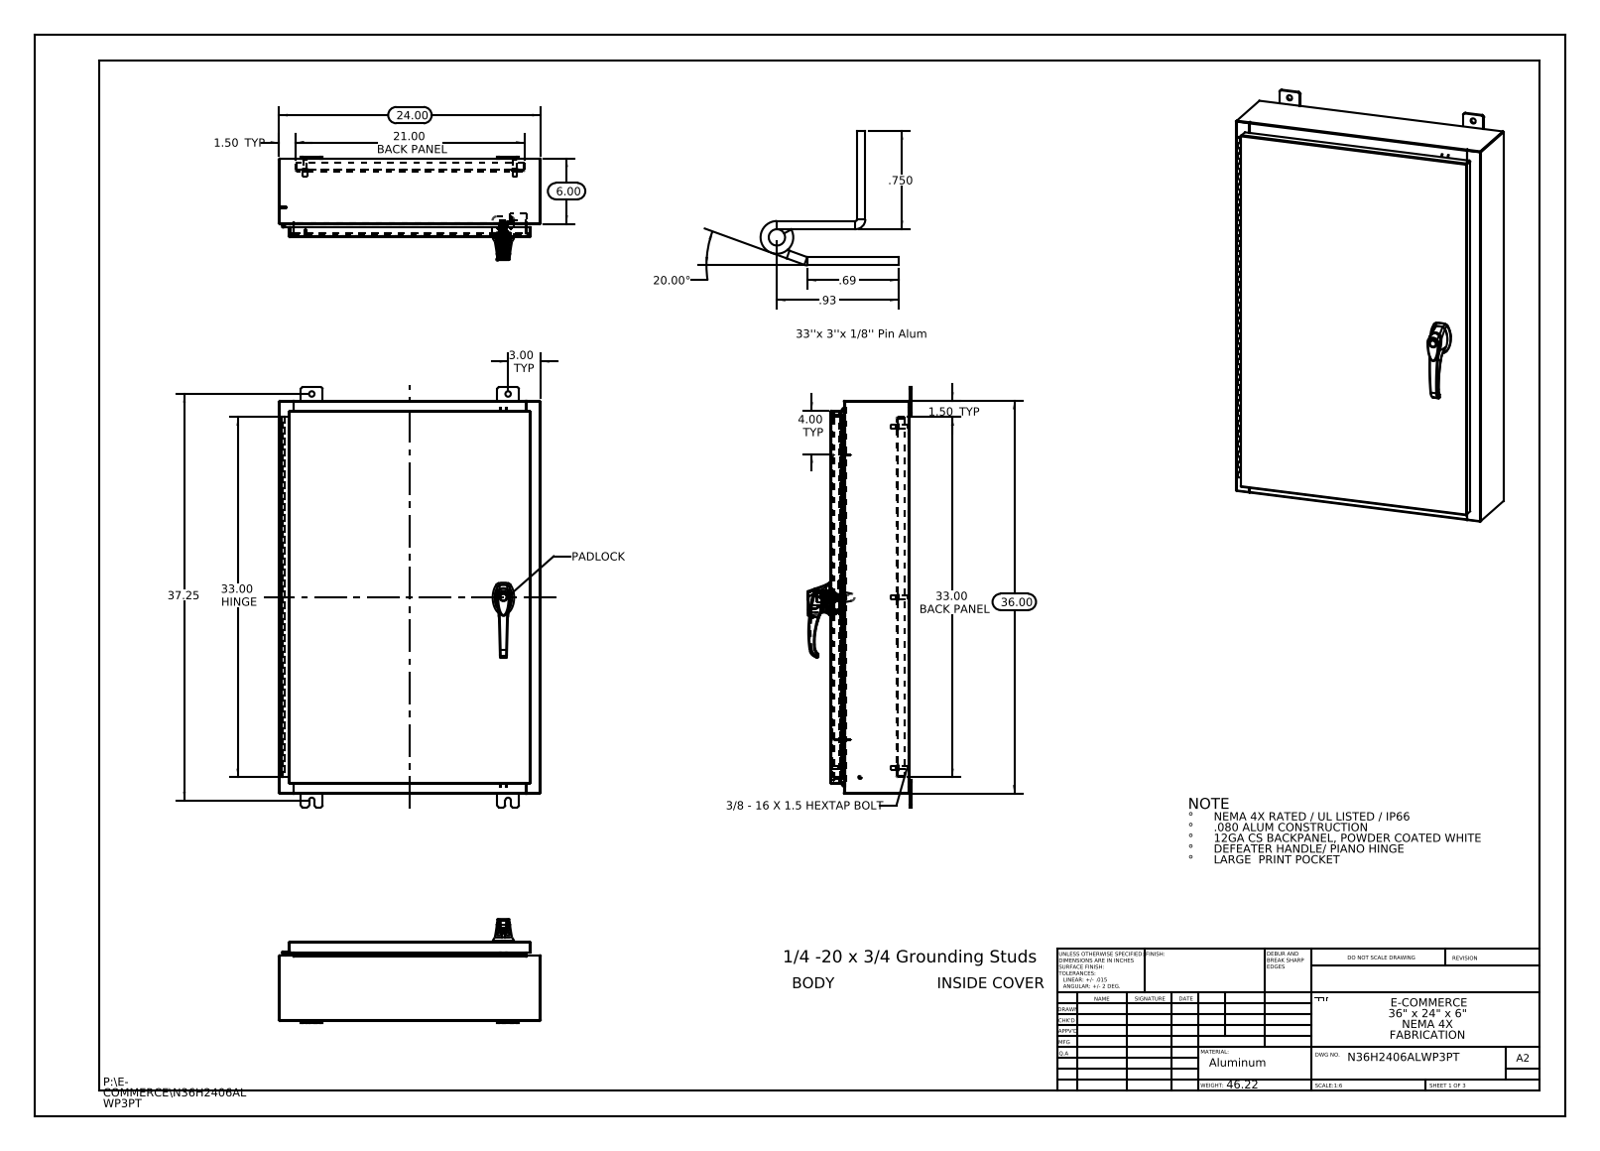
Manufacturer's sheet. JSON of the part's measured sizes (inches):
{"part_name": "26161102; 10_30 CD Stud; 022151; 00005090 (+8 more)", "step_written_by": "SolidWorks 2013 (CONFIG_CONTROL_DESIGN)", "units": "inches", "bodies": {"solids": 39, "faces": 2856, "planar": 1053, "cylindrical": 1085, "other": 718}, "overall_size": [38.5, 24, 9.495], "volume_in3": 300.7, "surface_area_in2": 7381, "round_holes": [[0.5, 10], [0.25, 4], [0.138, 3], [0.161, 3], [0.079, 2], [0.203, 2], [0.313, 2], [0.437, 2], [0.125, 1], [0.125, 1], [0.197, 1], [0.276, 1]], "round_bosses_or_shafts": [[0.625, 6], [0.375, 6], [0.33, 6], [0.157, 4], [0.14, 4], [0.315, 3], [0.236, 3], [1.181, 1]], "partial_cylinders_radius": [[0.118, 37], [0.006, 33], [0.013, 24], [0.19, 24], [0.088, 18], [0.039, 15], [0.028, 12], [0.008, 6]], "face_to_face_distances": [0.075, 7.126, 0.104, 7.051, 7.201, 1, 1.075, 6.051, 6.126, 1.179], "hole_center_spacings": [11.363, 13.669, 15.625, 24.793, 19.25, 0.295, 0.625, 0.841]}
